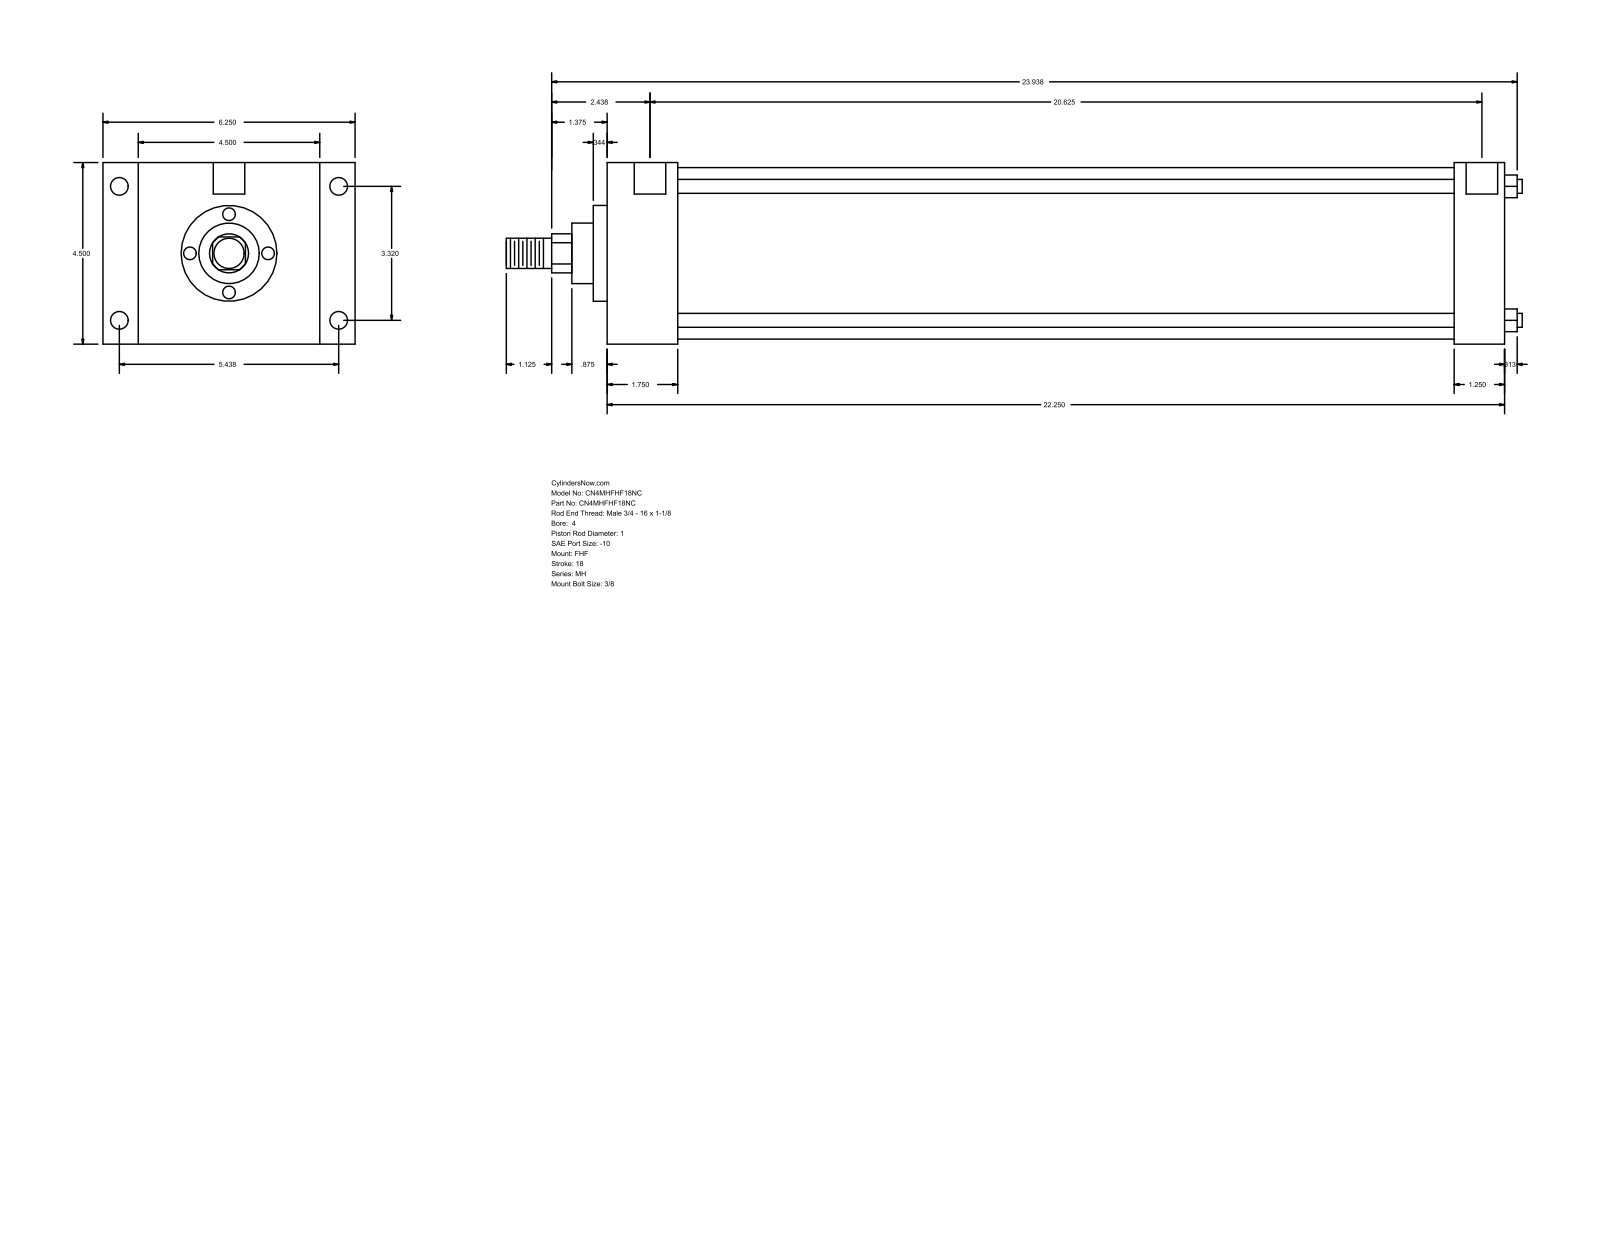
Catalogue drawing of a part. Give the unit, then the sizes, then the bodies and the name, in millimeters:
Units: millimetres
Overall size (bounding box): 639.76 × 158.75 × 114.3
Round holes (diameter × count): ⌀8.73 ×4, ⌀11.13 ×4, ⌀19.84 ×2
Round bosses / shafts (diameter × count): ⌀8.76 ×4, ⌀107.95 ×1, ⌀60.33 ×1, ⌀38.1 ×1, ⌀25.4 ×1, ⌀19.05 ×1
Partial cylindrical surfaces — rounded edges, fillets, slot ends (radius × count): R12.29 ×1
Main face-to-face distances: 114.3, 565.16, 44.46, 520.7, 22.23, 136.53, 158.76, 533.41, 488.95, 31.75
Hole centre spacings: 84.32, 138.12, 161.82, 527.05, 1.58, 1.59, 523.88, 525.46
Bodies: 0 solids, 90 faces (61 planar, 29 cylindrical, 0 other)
Part name (STEP PRODUCT): MH_FHF__0400_1
STEP written by: GSSL Pune (CONFIG_CONTROL_DESIGN)
